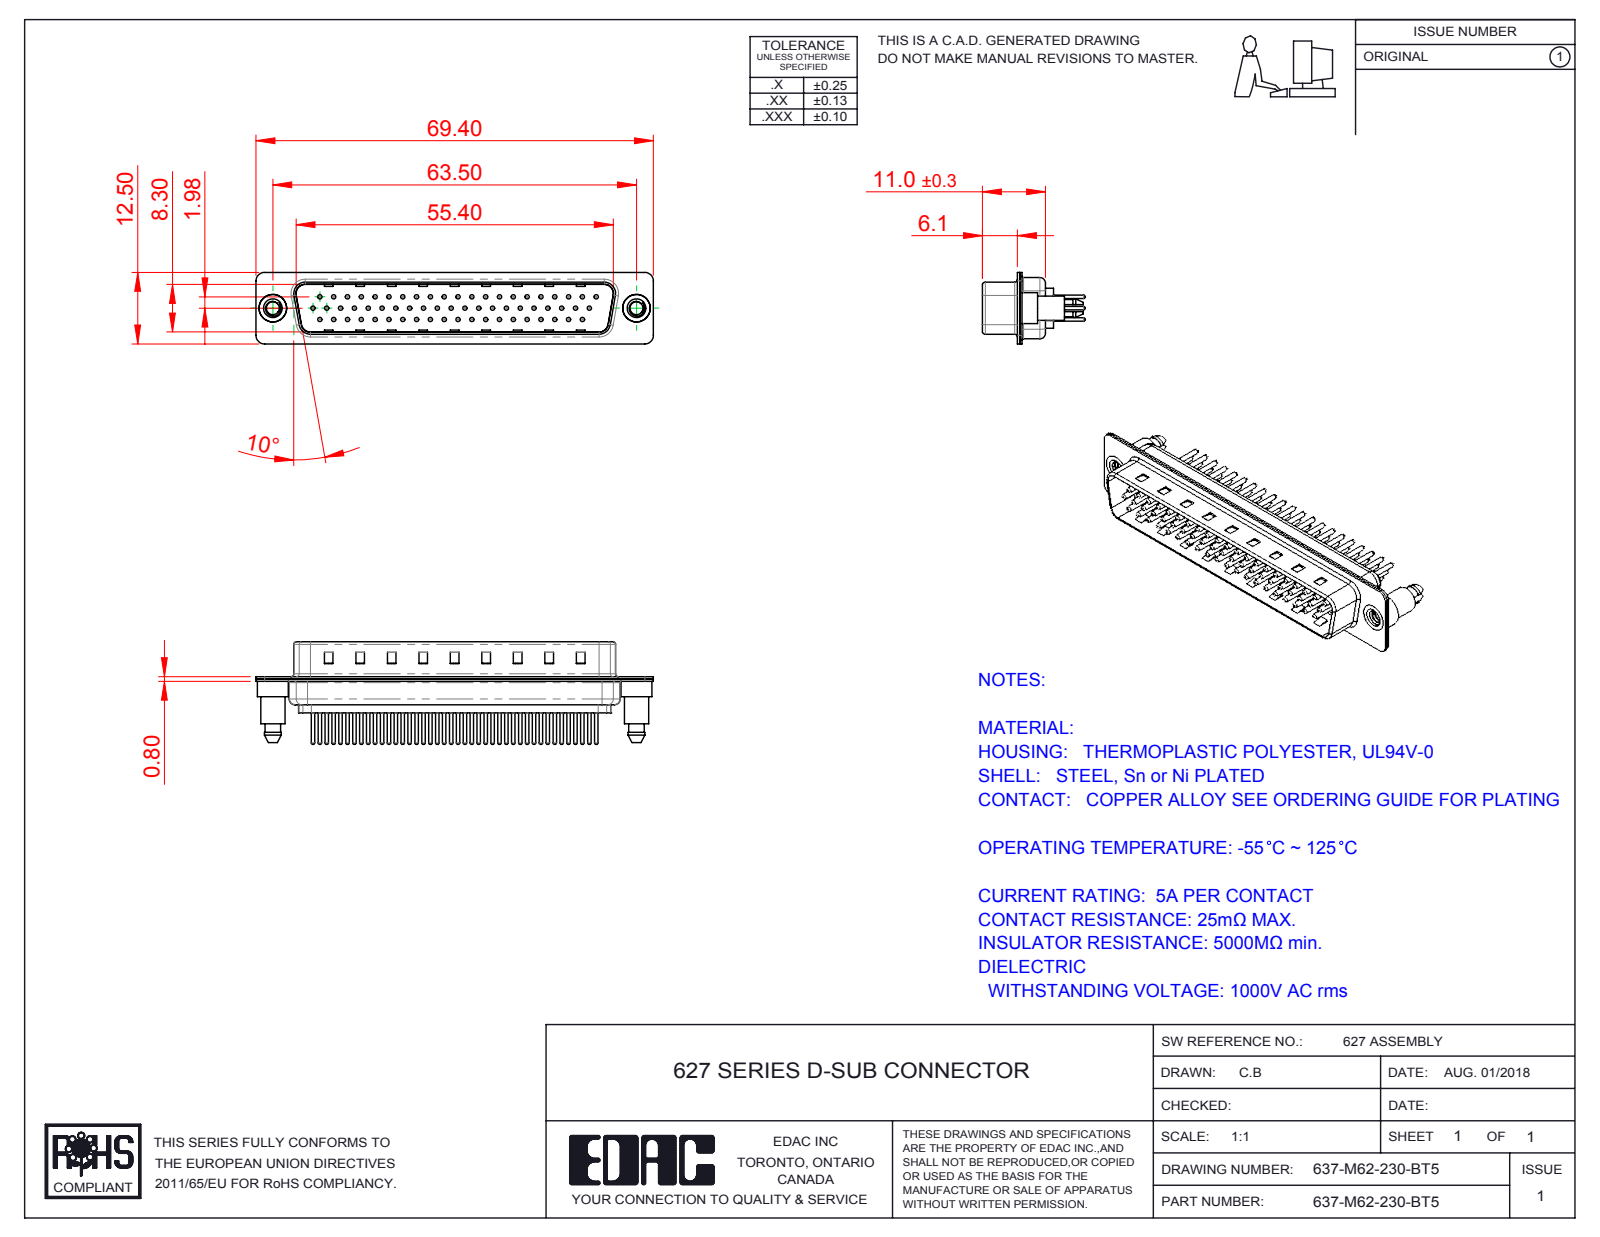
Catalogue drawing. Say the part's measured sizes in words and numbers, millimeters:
The part is named "637M Housing_62 Contacts; 637M 4-40 Threaded Boardlock; 637M Shell Rear_62 Contacts; 637M Contact Row 1_30 (+4 more)". Its 3-D file was written by "SolidWorks 2016 (CONFIG_CONTROL_DESIGN)". It is 67 solids with 2756 faces: 653 planar, 1041 cylindrical and 1062 other. Overall it measures 69.4 by 17.9 by 12.5 millimeters. Its volume is 4 051 cubic millimeters and its surface area 11 746 square millimeters. Round holes: 62 of diameter 0.75, 62 of diameter 1.6, 62 of diameter 2, 2 of diameter 2.26, 2 of diameter 4, 2 of diameter 4.8. Round bosses or shafts: 62 of diameter 1.5, 62 of diameter 0.6, 2 of diameter 5.4, 2 of diameter 4.9, 2 of diameter 4.25. Partial cylindrical surfaces (rounded edges, fillets, slot ends): 18 of radius 1.5, 12 of radius 2, 10 of radius 1.6, 8 of radius 0.5, 4 of radius 0.25, 4 of radius 0.6, 4 of radius 0.65, 4 of radius 0.9. The main face-to-face distances are 0.4, 0.8, 9.5, 9.1, 8.7, 9.9, 0.75, 0.35, 5.9, 1.2. The hole center spacings are 7.24, 2.32, 2.41, 4.13, 9.65, 4.83, 14.48, 11.04.
